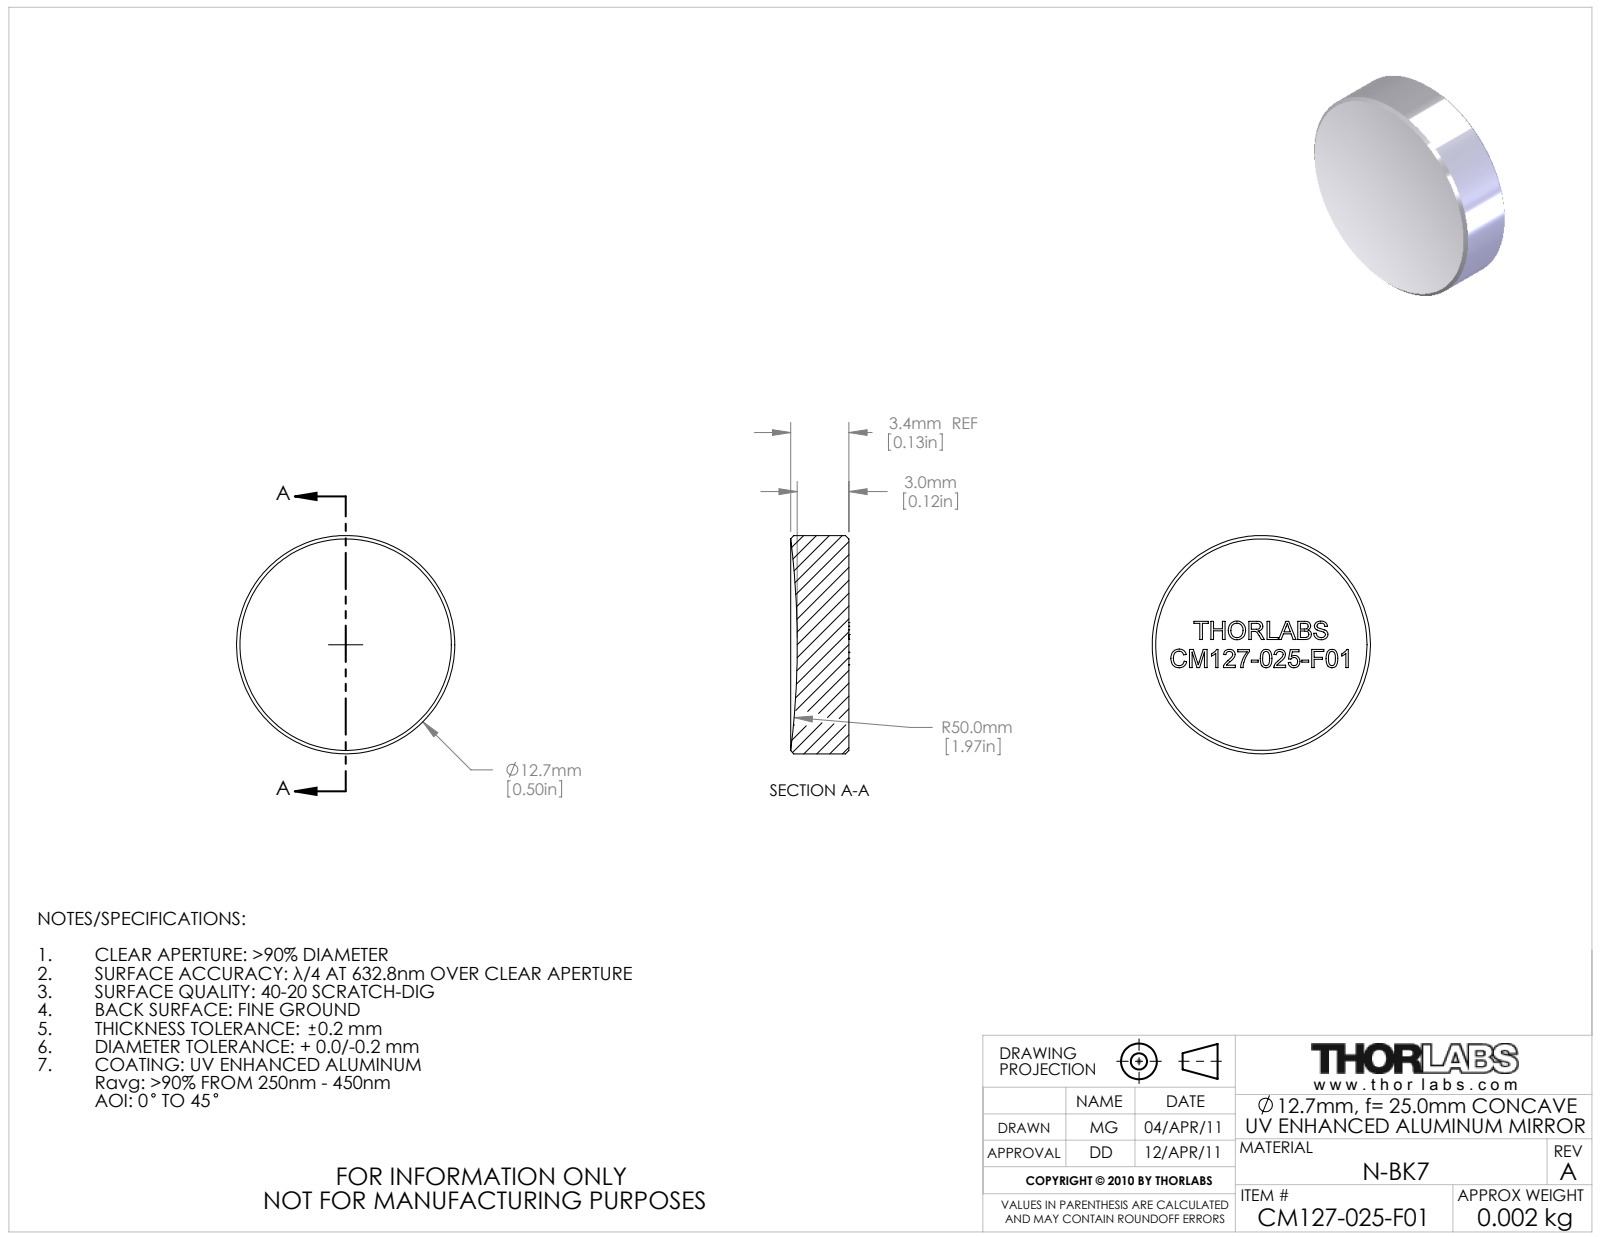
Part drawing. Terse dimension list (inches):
name: 22192-E0W
written by: SolidWorks 2011 (AUTOMOTIVE_DESIGN)
unit: in
bodies: 1 solid, 265 faces (151 planar, 2 cylindrical, 112 other)
size: 0.5 × 0.5 × 0.133
volume: 0.025 in³; area: 0.588 in²
bosses: 1× ⌀0.5
face distances: 0.042, 0.064, 0.036, 0.052, 0.041, 0.024, 0.065, 0.112, 0.06, 0.026
